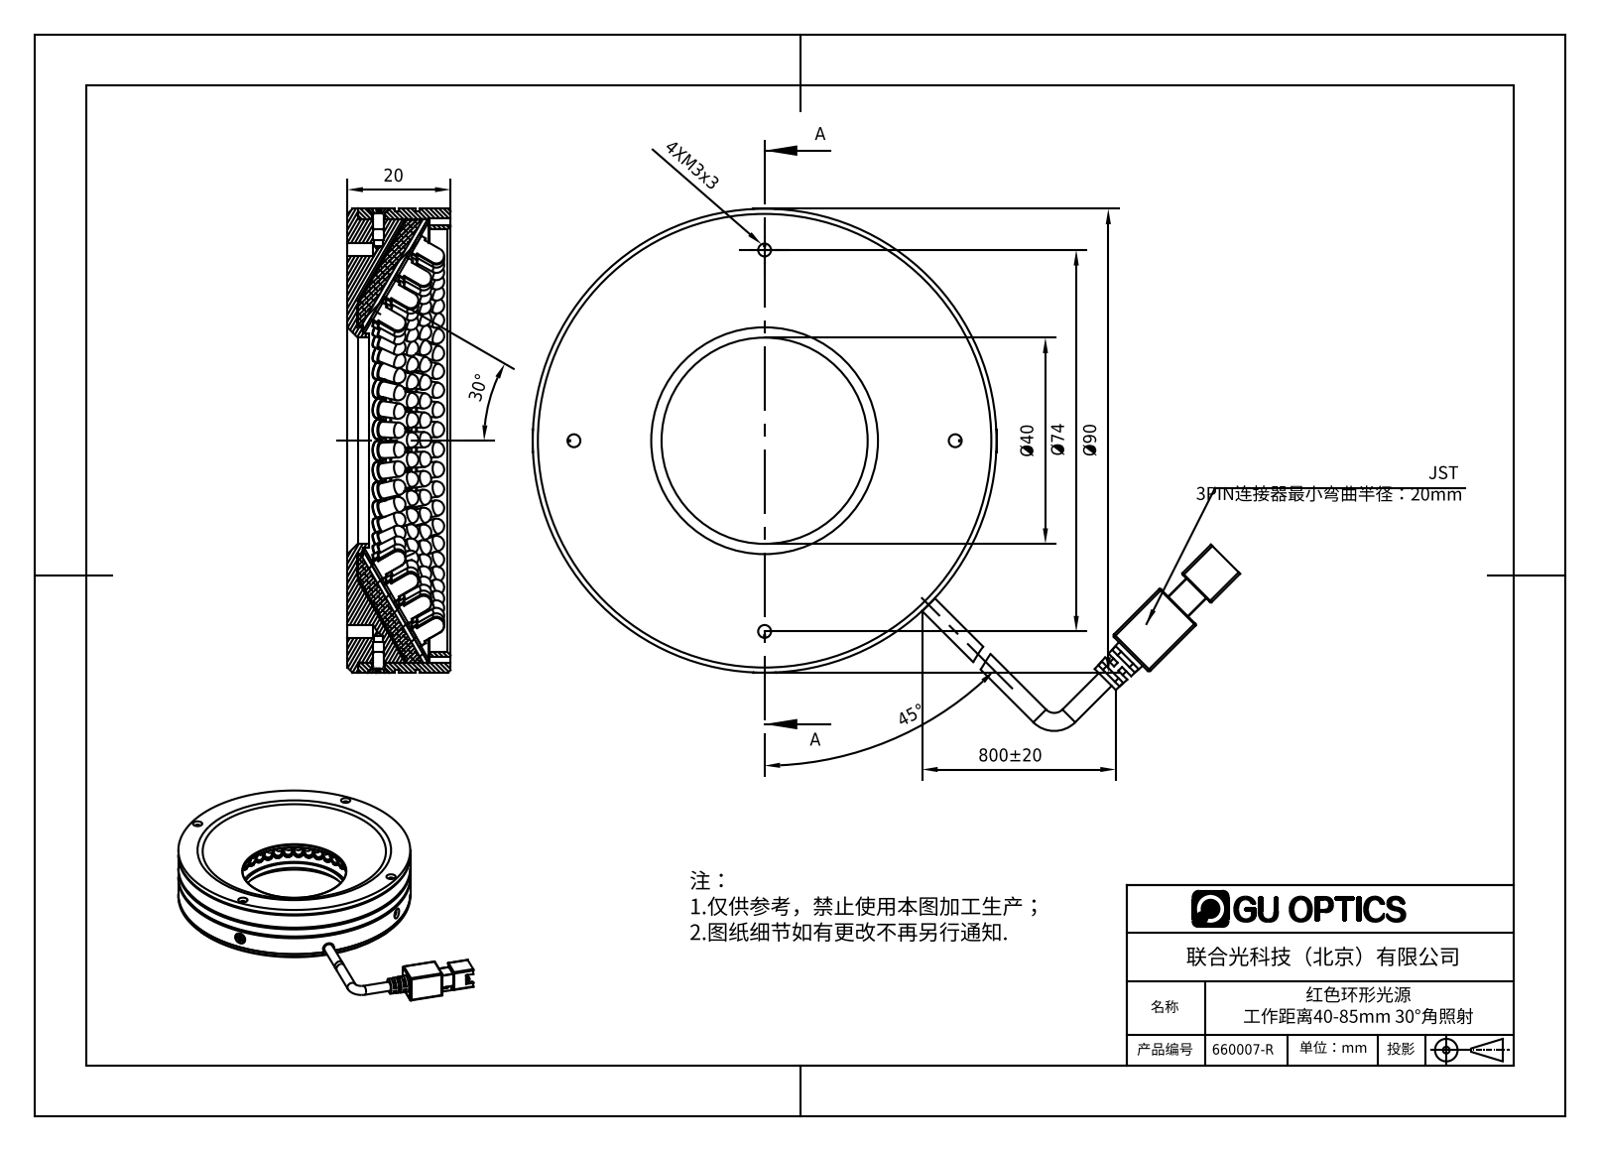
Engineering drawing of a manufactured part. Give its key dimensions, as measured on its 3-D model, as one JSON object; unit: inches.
{"part_name": "660007-R", "step_written_by": "SolidWorks 2016 (AUTOMOTIVE_DESIGN)", "units": "inches", "bodies": {"solids": 201, "faces": 4314, "planar": 2669, "cylindrical": 1337, "other": 308}, "overall_size": [5.405, 3.989, 0.951], "volume_in3": 4.808, "surface_area_in2": 122, "round_holes": [[0.049, 4], [0.071, 4], [0.098, 4], [0.063, 2], [0.079, 2], [0.094, 2], [1.575, 1], [1.732, 1], [3.228, 1]], "round_bosses_or_shafts": [[0.15, 248], [0.118, 192], [0.138, 2], [3.543, 1], [3.504, 1], [3.386, 1], [1.756, 1], [1.642, 1]], "partial_cylinders_radius": [[0.008, 37], [0.004, 15], [0.016, 12], [0.012, 1], [0.027, 1], [0.055, 1], [0.065, 1], [0.354, 1]], "face_to_face_distances": [0.787, 0.079, 0.866, 0.709, 0.039, 0.02, 0.157, 0.236, 0.118, 0.551], "hole_center_spacings": [0.217, 1.673, 2.219, 3.13, 3.346, 2.366, 1.457, 2.06]}
